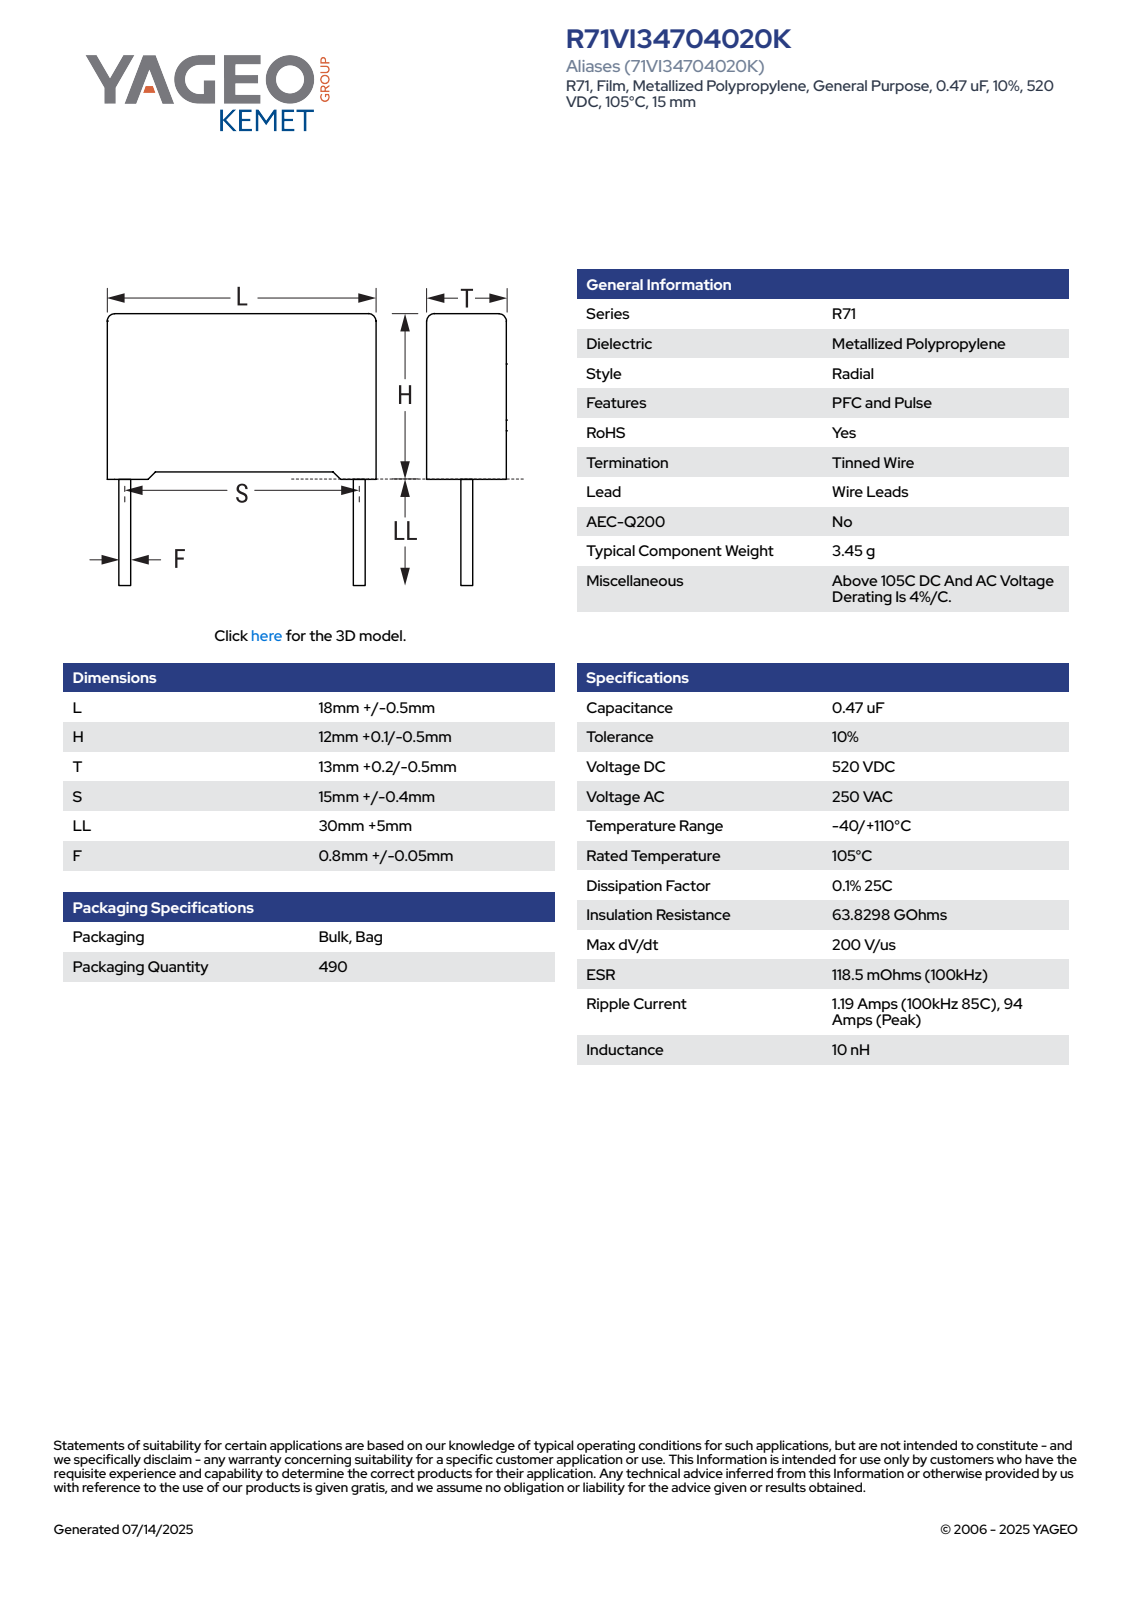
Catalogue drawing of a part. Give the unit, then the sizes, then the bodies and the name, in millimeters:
Units: millimetres
Overall size (bounding box): 47.1 × 18.5 × 13.21
Round bosses / shafts (diameter × count): ⌀0.85 ×2
Partial cylindrical surfaces — rounded edges, fillets, slot ends (radius × count): R0.5 ×4
Main face-to-face distances: 13.2, 11.35, 18.5, 0.62, 0.75, 12.1, 17.88, 12.58, 0.42, 0.33
Volume: 2 831 mm³ · Surface area: 1 484 mm²
Bodies: 4 solids, 85 faces (77 planar, 8 cylindrical, 0 other)
Part name (STEP PRODUCT): CFR_RB2_18X12X13_L18.5H12.1T13.2S15LL35F0.85
STEP written by: SolidWorks 2021 (AUTOMOTIVE_DESIGN)
